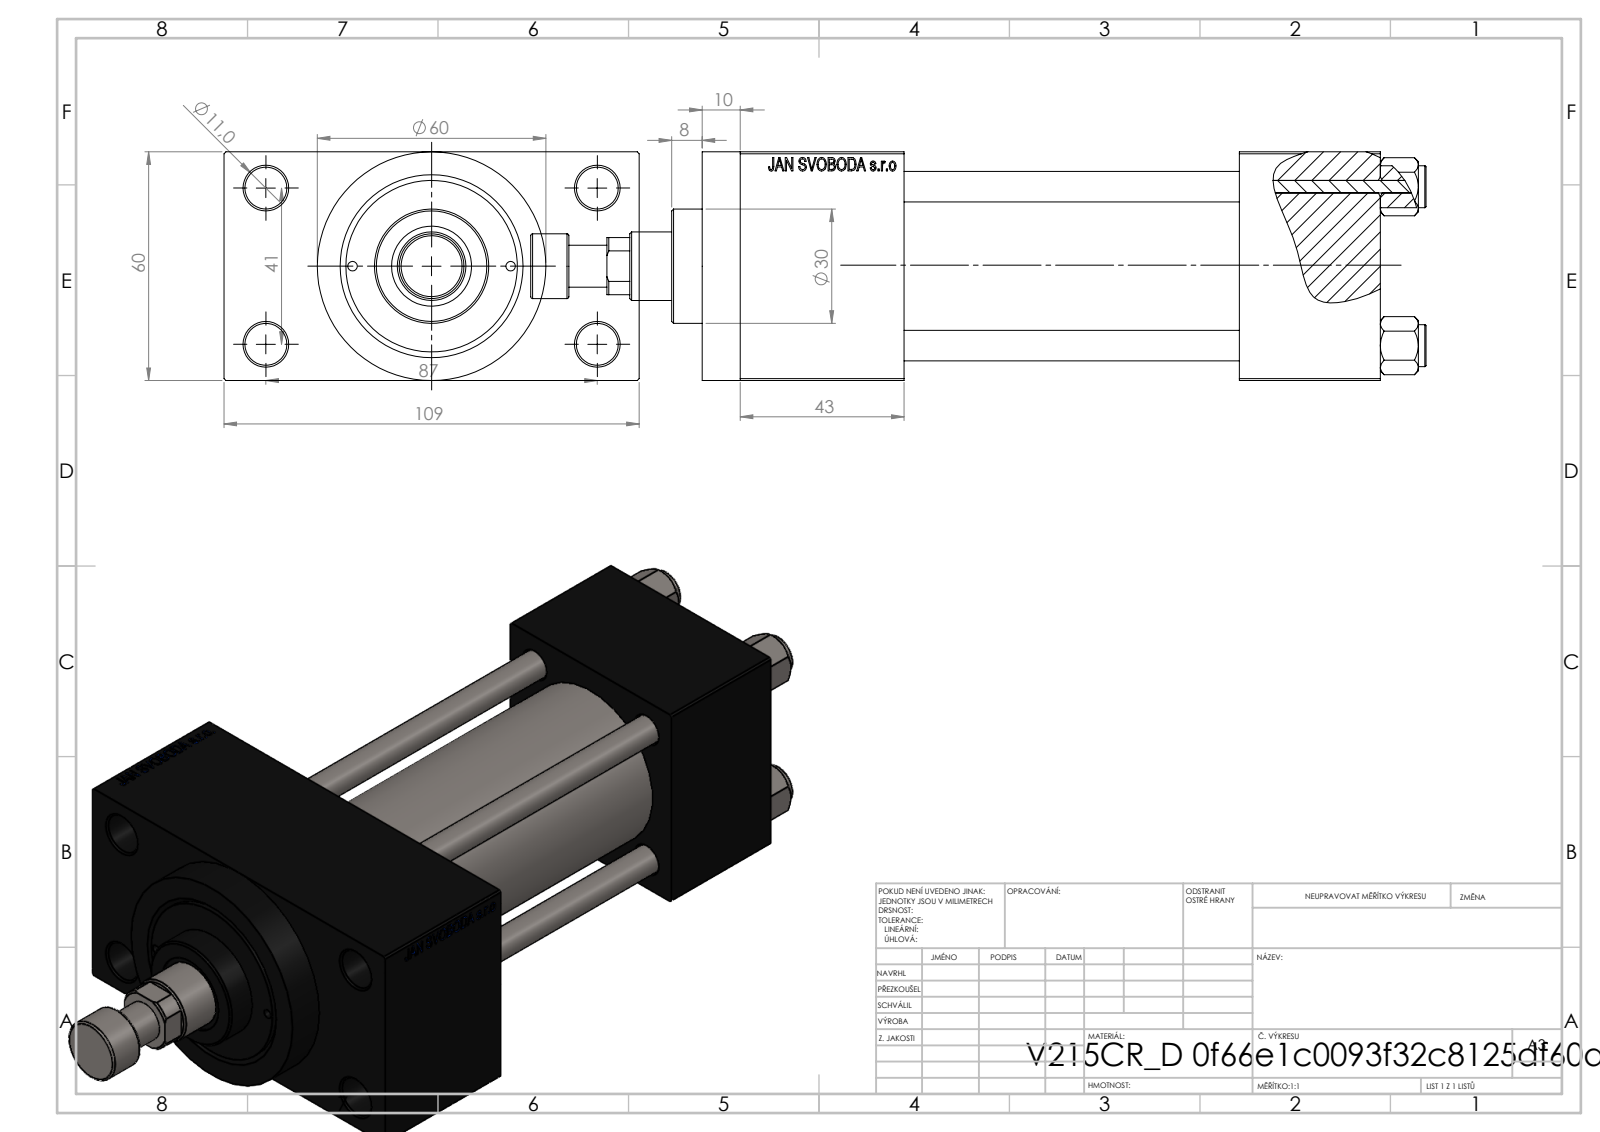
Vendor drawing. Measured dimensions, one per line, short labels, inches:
name: V215CR_ROD_END_F; V215CR_VCP_D; NUT_M5_D; V215CR_D_Body (+2 more)
written by: SolidWorks 2019 (CONFIG_CONTROL_DESIGN)
unit: in
bodies: 12 solids, 1123 faces (503 planar, 96 cylindrical, 524 other)
size: 9.252 × 4.291 × 2.362
volume: 33.04 in³; area: 211.8 in²
holes: 4× ⌀0.315, 4× ⌀0.433, 2× ⌀0.098, 2× ⌀0.276, 2× ⌀0.656, 2× ⌀0.945, 1× ⌀0.335, 1× ⌀0.709, 1× ⌀0.827, 1× ⌀1.22, 1× ⌀1.575, 1× ⌀1.772
bosses: 5× ⌀0.433, 1× ⌀2.362, 1× ⌀1.811, 1× ⌀1.181, 1× ⌀0.669
face distances: 2.362, 3.465, 0.965, 1.457, 3.327, 4.921, 6.614, 5.157, 1.693, 0.394
hole spacings: 0.821, 0.892, 1.161, 1.206, 1.642, 1.832, 1.856, 1.893
